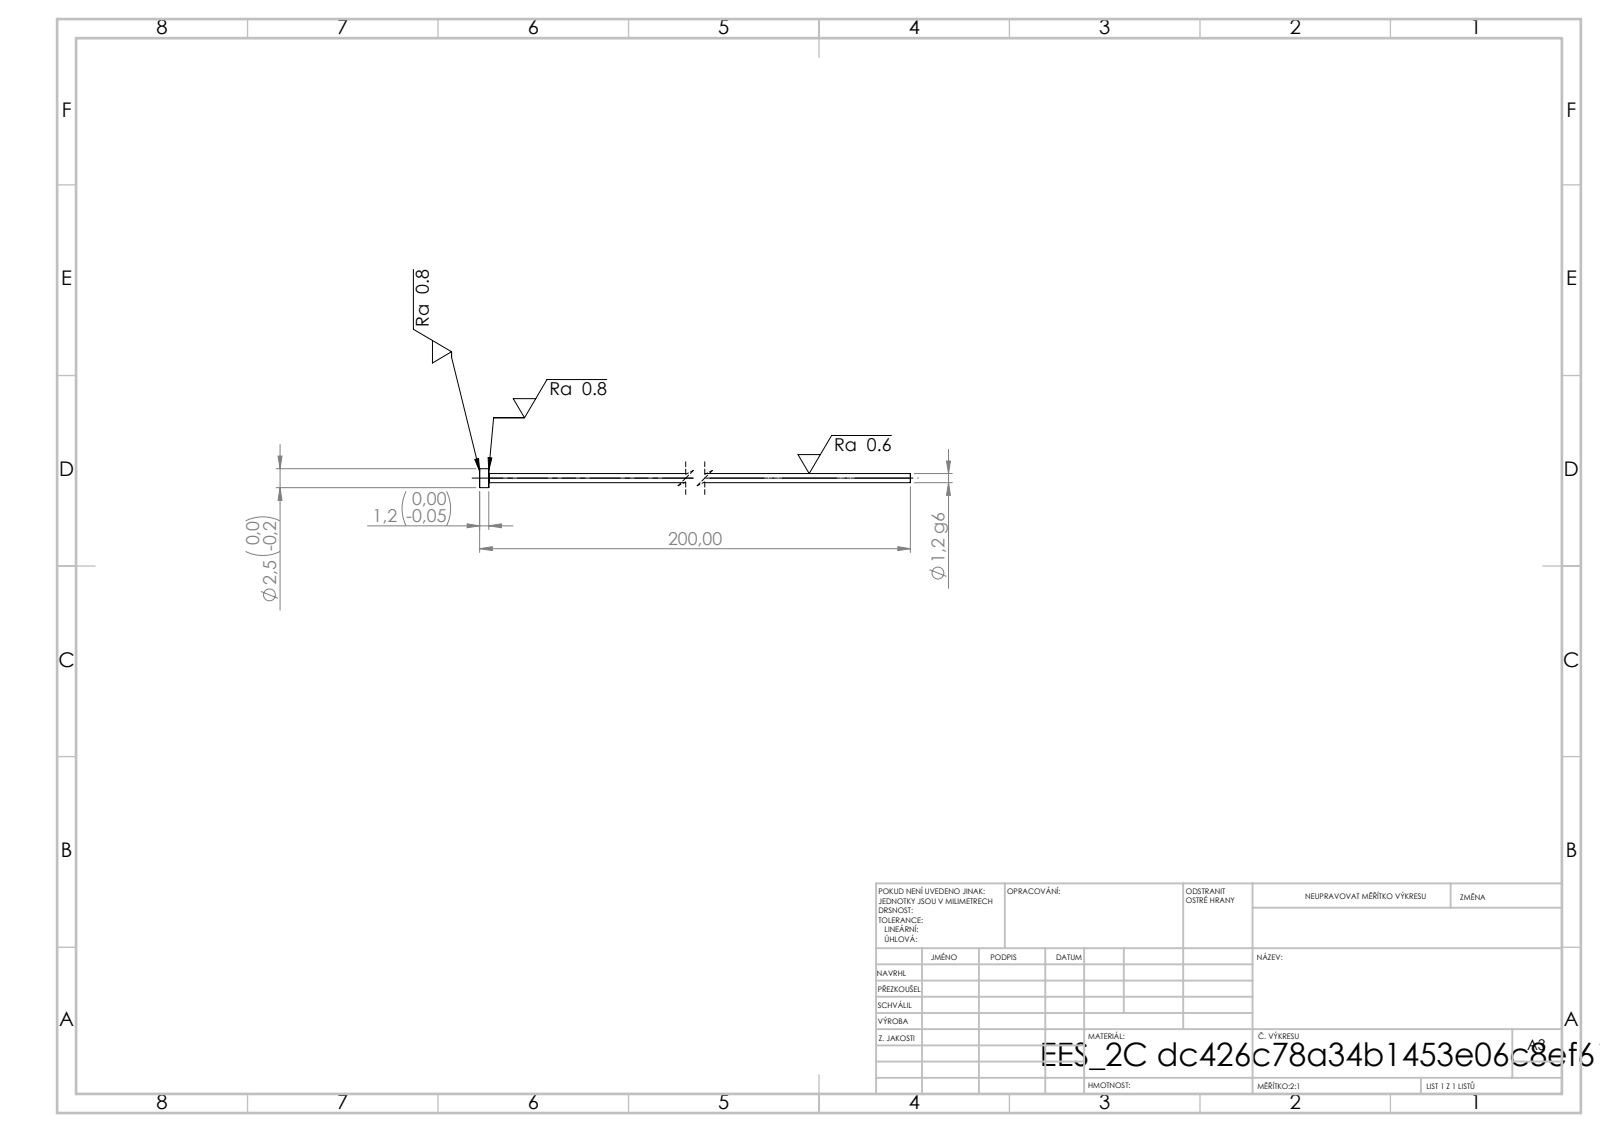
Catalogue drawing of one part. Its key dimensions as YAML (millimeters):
step_written_by: "SolidWorks 2019 (CONFIG_CONTROL_DESIGN)"
units: millimeters
bodies: {solids: 1, faces: 7, planar: 3, cylindrical: 4, other: 0}
overall_size: [200, 2.5, 2.5]
volume: 231
surface_area: 769
round_bosses_or_shafts:
  - {diameter: 2.5, count: 1}
  - {diameter: 1.2, count: 1}
face_to_face_distances: [1.2, 200, 198.8]
